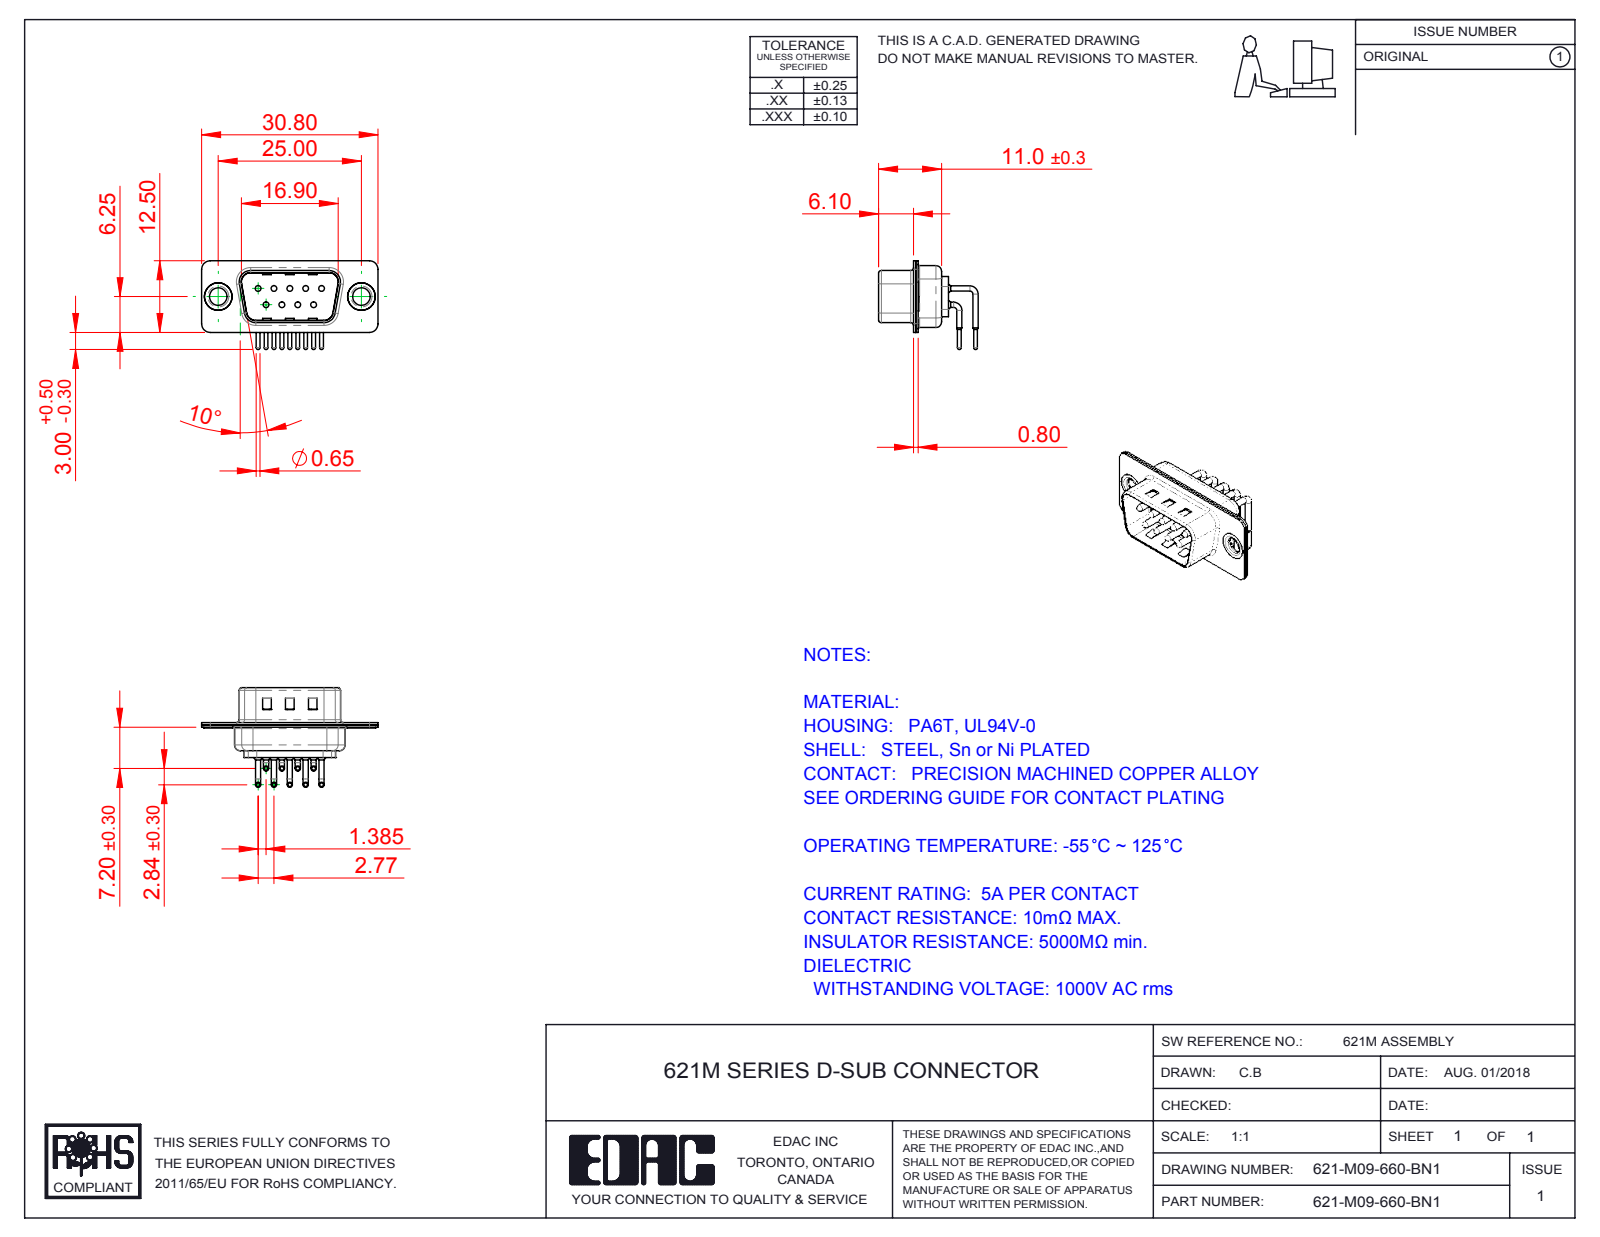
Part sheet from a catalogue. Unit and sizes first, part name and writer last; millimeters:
Units: millimetres
Overall size (bounding box): 30.8 × 17.39 × 15.49
Round holes (diameter × count): ⌀1 ×9, ⌀1.7 ×9, ⌀2 ×9, ⌀3.05 ×2, ⌀4 ×2, ⌀4.8 ×2
Round bosses / shafts (diameter × count): ⌀0.9 ×18, ⌀1.5 ×9, ⌀0.65 ×9, ⌀5 ×2, ⌀4.9 ×2, ⌀3.55 ×2
Partial cylindrical surfaces — rounded edges, fillets, slot ends (radius × count): R1.5 ×16, R2 ×12, R1.01 ×9, R0.5 ×8, R1.6 ×8, R0.25 ×4, R0.6 ×4, R0.65 ×4
Main face-to-face distances: 0.4, 0.85, 0.8, 9.55, 1.25, 10.4, 8.7, 0.35, 6.1, 5.7
Hole centre spacings: 3.16, 2.77, 5.54, 5.03, 5.04, 8.31, 7.1, 7.48
Volume: 1 289 mm³ · Surface area: 3 701 mm²
Bodies: 14 solids, 1268 faces (683 planar, 437 cylindrical, 148 other)
Part name (STEP PRODUCT): 621M Housing_09 Contacts; 621M Shell Rear_09 Contacts; 621M Shell Front_09 Contacts; 621M Thru Hole Rivet (+3 more)
STEP written by: SolidWorks 2016 (CONFIG_CONTROL_DESIGN)
